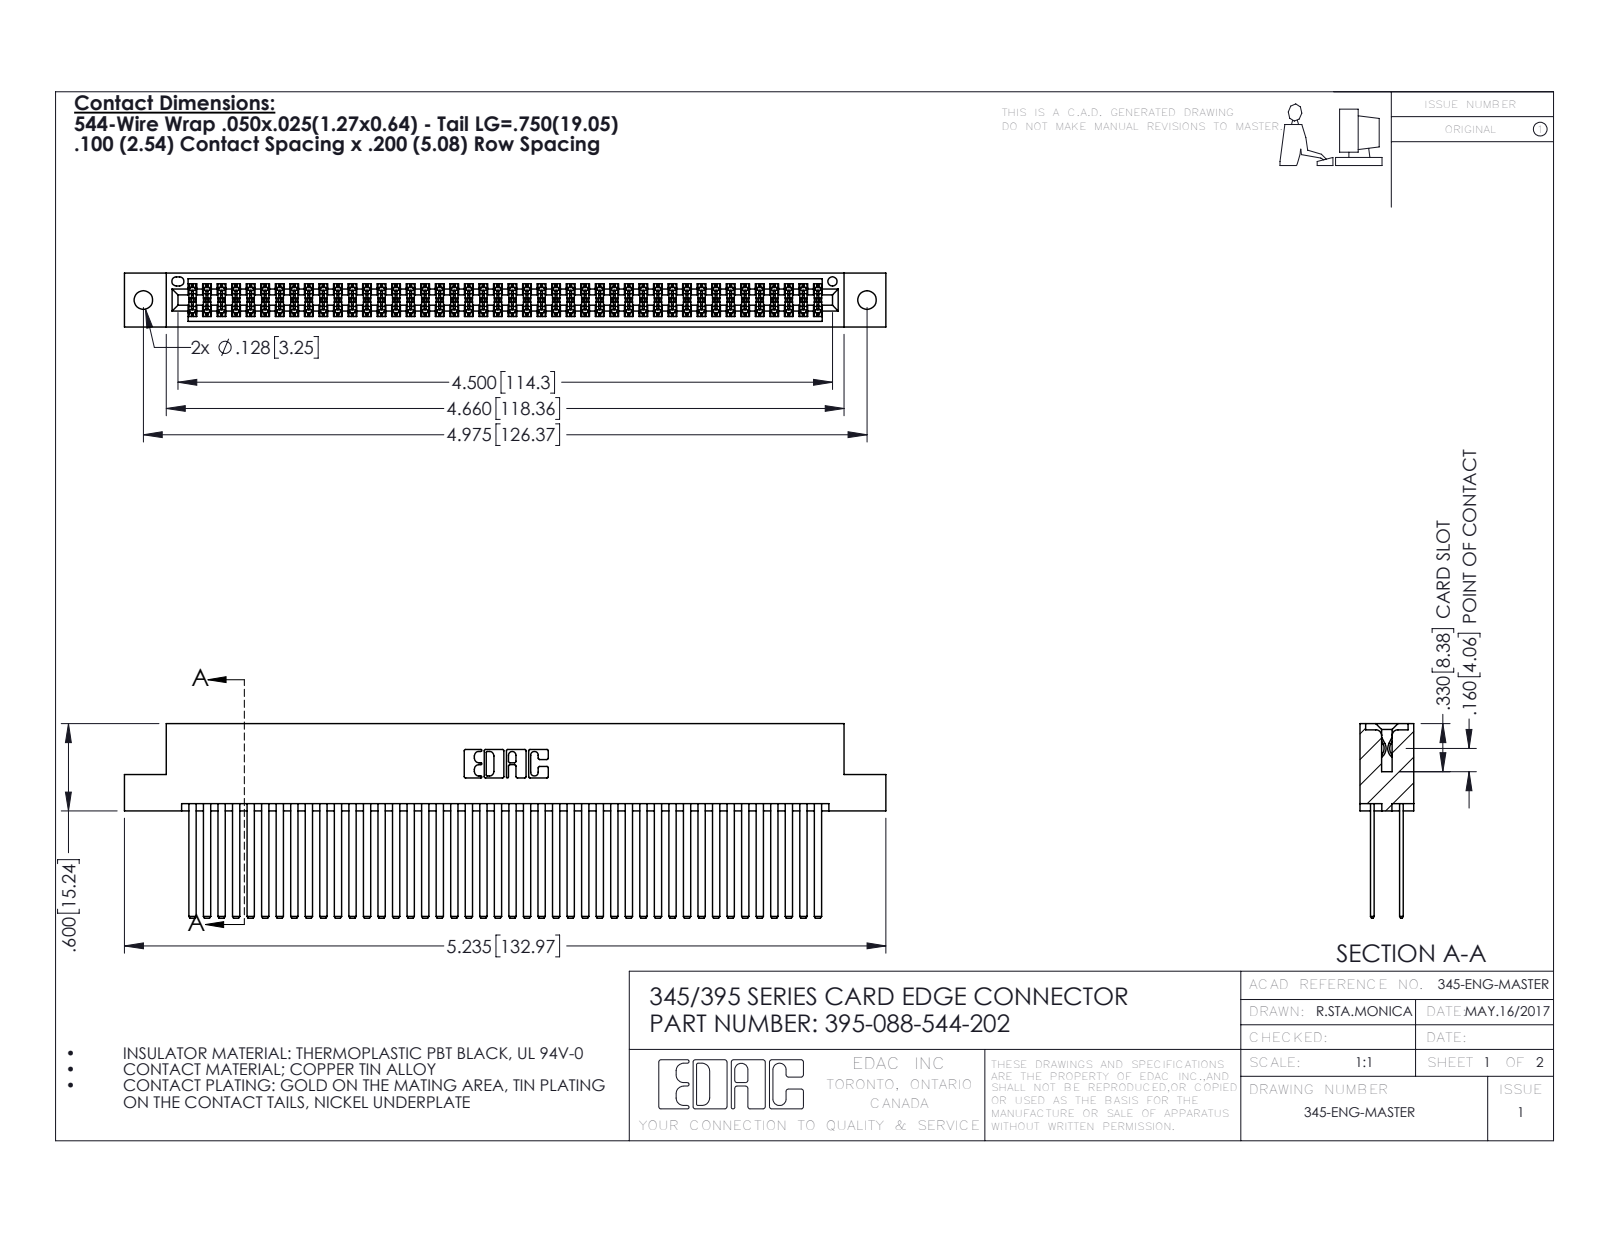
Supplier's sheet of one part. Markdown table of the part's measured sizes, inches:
| quantity | value |
| --- | --- |
| part name | 345 Part_Flush Mounting Lugs - 0.128 Dia; 345-292-001_345-293-144; 395-088-544-202 |
| STEP written by | SolidWorks 2016 (CONFIG_CONTROL_DESIGN) |
| units | inches |
| bodies | 89 solids, 3998 faces (2632 planar, 1366 cylindrical, 0 other) |
| overall size | 5.235 × 1.337 × 0.37 |
| volume | 0.862 in³ |
| surface area | 37.62 in² |
| round holes (diameter × count) | 0.128 × 2, 0.064 × 1 |
| partial cylindrical surfaces (radius × count) | 0.006 × 132, 0.01 × 22, 0.007 × 6, 0.031 × 6, 0.026 × 3, 0.014 × 2, 0.019 × 2, 0.022 × 2 |
| main face-to-face distances | 0.2, 0.025, 0.298, 0.072, 0.098, 0.272, 0.225, 0.175, 0.37, 0.05 |
| hole center spacings | 0.27, 4.739, 4.975 |
